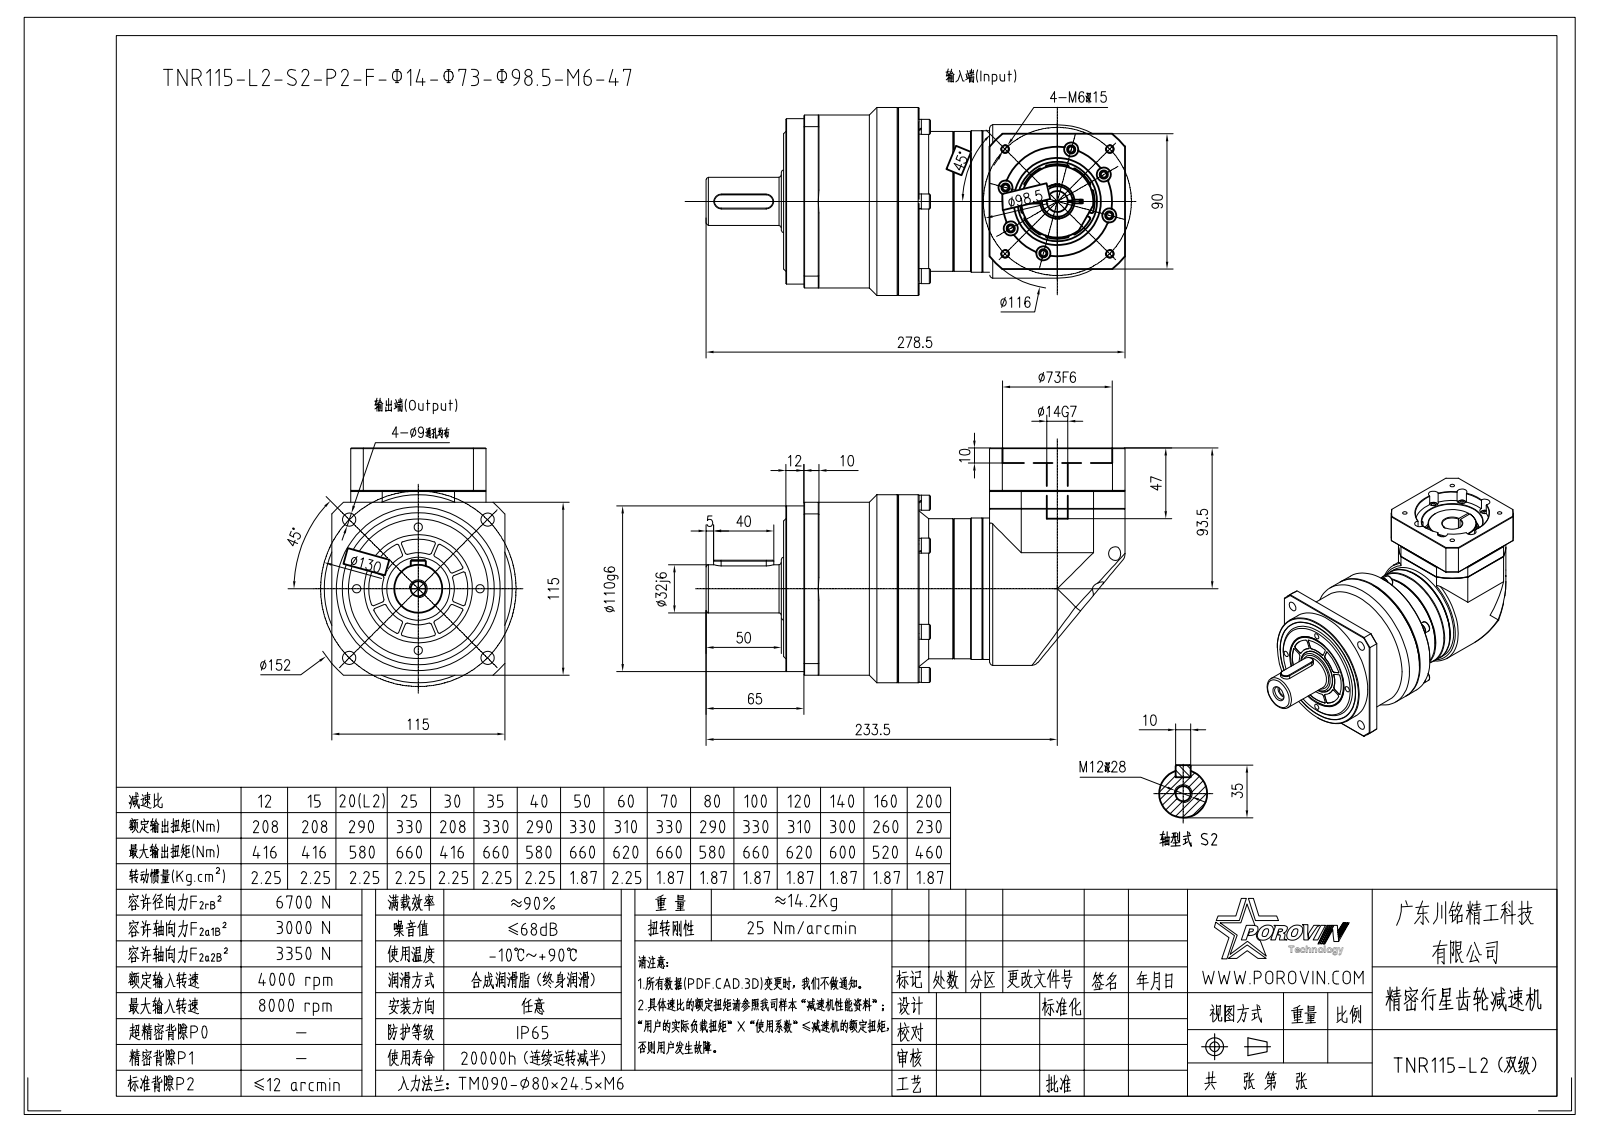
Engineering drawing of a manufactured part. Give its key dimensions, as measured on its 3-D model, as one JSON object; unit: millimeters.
{"part_name": "HEXAGON_SOCKET_HEAD_CAP_SC-2428; TNS1150001; SPRING_LOCK_WASHERS--NORMA-2483; HEXAGON_SOCKET_HEAD_CAP_S-24794 (+8 more)", "step_written_by": "CREO PARAMETRIC BY PTC INC, 2020053 (CONFIG_CONTROL_DESIGN)", "units": "millimeters", "bodies": {"solids": 63, "faces": 1656, "planar": 683, "cylindrical": 659, "other": 314}, "overall_size": [278.5, 156, 125], "volume_mm3": 2192000, "surface_area_mm2": 286029, "round_holes": [[5.5, 23], [5.4, 19], [9.5, 12], [5, 9], [9.2, 7], [4.2, 6], [6.6, 6], [6.68, 6], [9, 4], [10.2, 2], [6.5, 1], [13, 1]], "round_bosses_or_shafts": [[8.5, 19], [8, 19], [5, 19], [10, 7], [6, 7], [9.88, 6], [125, 1], [115, 1]], "partial_cylinders_radius": [[1, 76], [5, 3], [4, 1], [5.25, 1], [36.5, 1], [51, 1], [58, 1], [76, 1]], "face_to_face_distances": [37, 90, 19.5, 12, 56.5, 56.3, 19.3, 137, 10, 2.5], "hole_center_spacings": [35.75, 57.25, 40.75, 46.18, 98.8, 46.25, 58.16, 61.92]}
